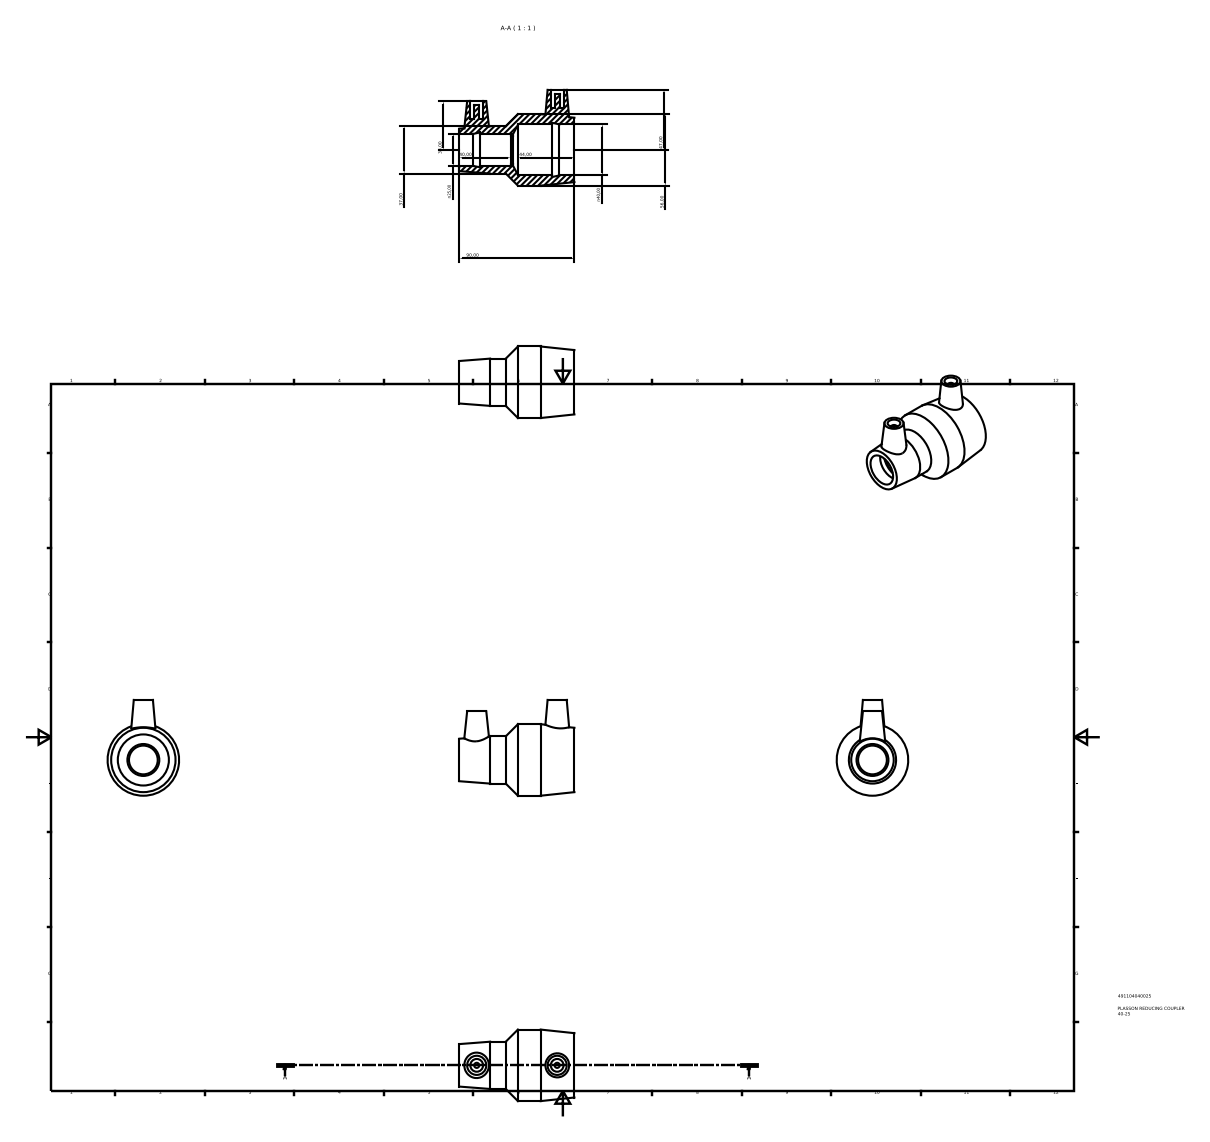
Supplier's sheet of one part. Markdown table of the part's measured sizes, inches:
| quantity | value |
| --- | --- |
| part name | 491104040025 |
| STEP written by | Autodesk Inventor 2015 (AUTOMOTIVE_DESIGN) |
| units | inches |
| bodies | 1 solid, 31 faces (12 planar, 11 cylindrical, 8 other) |
| overall size | 3.543 × 2.953 × 2.205 |
| volume | 5.087 in³ |
| surface area | 43.65 in² |
| round holes (diameter × count) | 0.394 × 2, 0.886 × 1, 0.984 × 1, 1.575 × 1 |
| round bosses / shafts (diameter × count) | 0.157 × 2, 2.205 × 1, 1.457 × 1 |
| main face-to-face distances | 3.543, 0.354, 2.85, 0.693, 0.551, 0.079, 1.654, 1.197, 1.89, 1.575 |
| hole center spacings | 2.48 |
